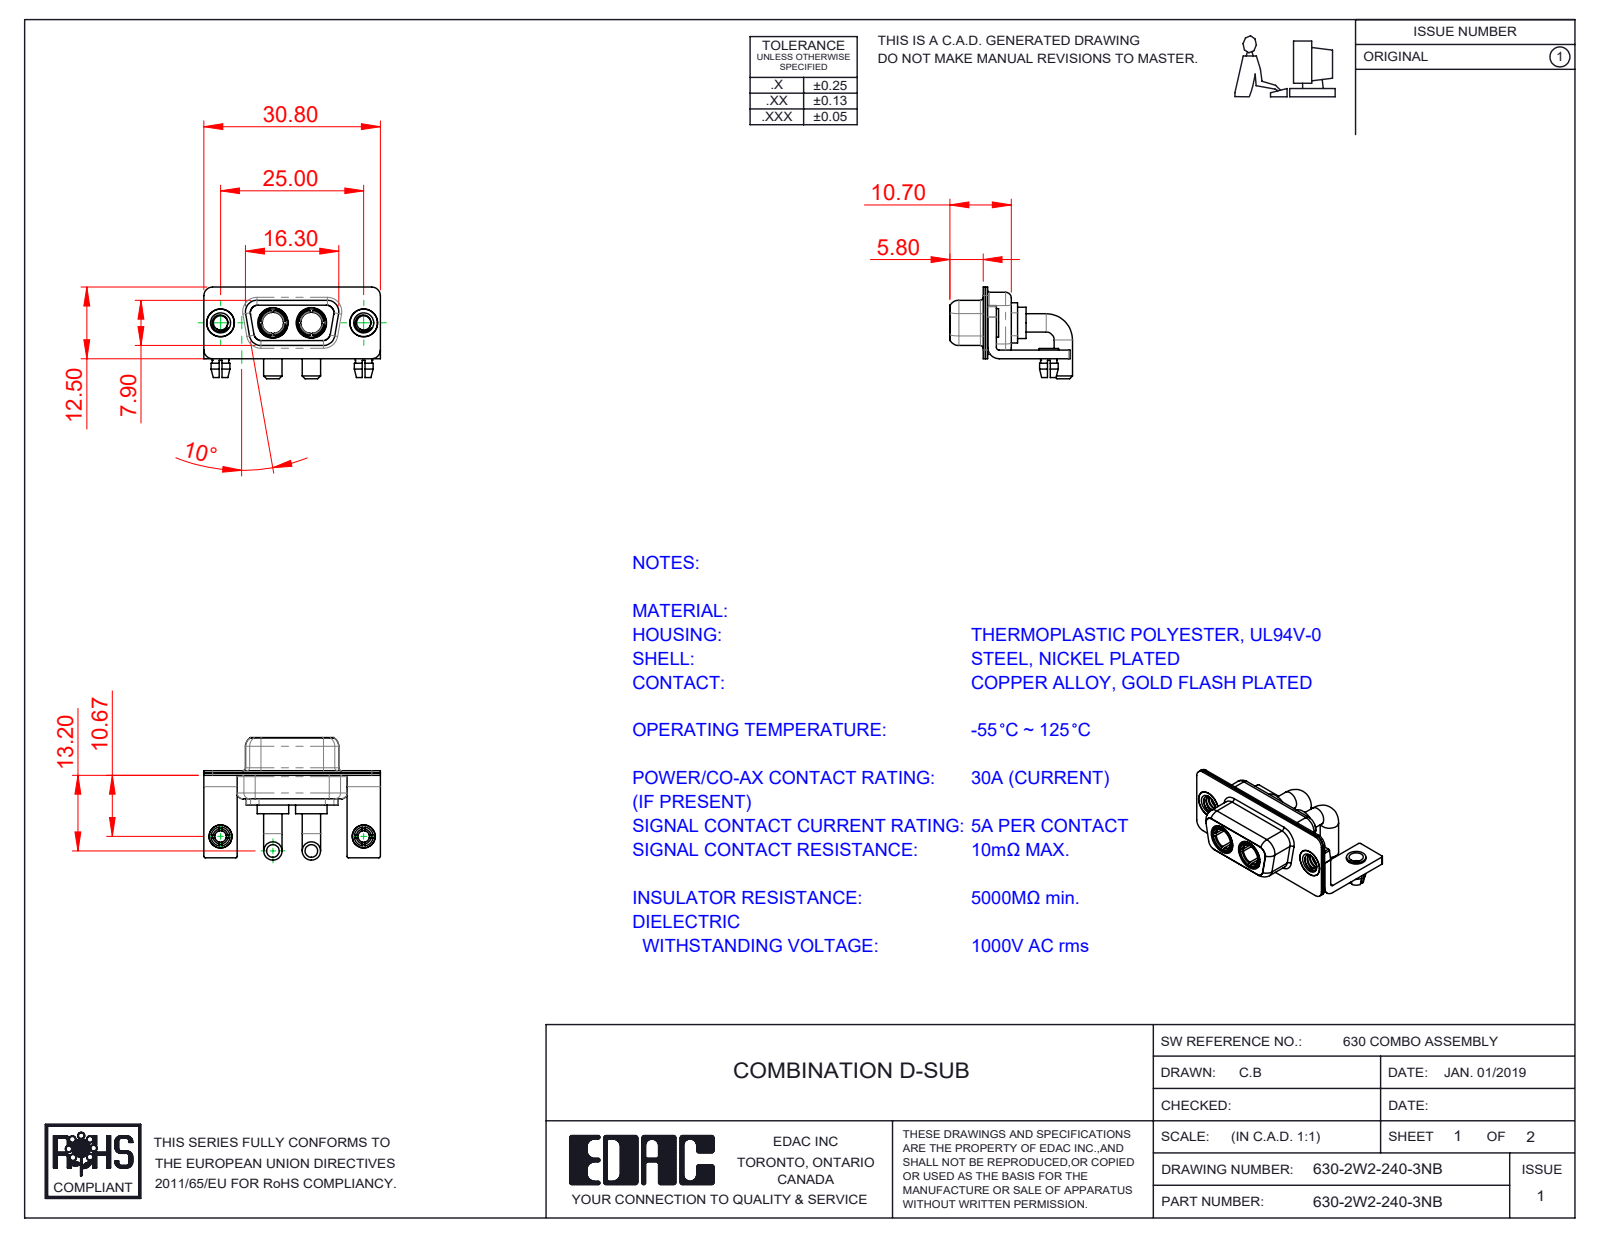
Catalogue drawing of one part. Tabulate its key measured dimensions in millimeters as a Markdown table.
| quantity | value |
| --- | --- |
| part name | 630Combo Shell Rear_09 Contacts; 630Combo Shell Front_09 Contacts; 630Combo Stabilizer Bracket; 630Combo Housing_2W2 (+4 more) |
| STEP written by | SolidWorks 2020 (CONFIG_CONTROL_DESIGN) |
| units | millimeters |
| bodies | 13 solids, 565 faces (193 planar, 237 cylindrical, 135 other) |
| overall size | 30.8 × 21.4 × 16 |
| volume | 2 161 mm³ |
| surface area | 5 228 mm² |
| round holes (diameter × count) | 2.5 × 4, 4.85 × 4, 2 × 2, 3.2 × 2, 3.7 × 2, 4 × 2, 4.05 × 2, 5.3 × 2 |
| round bosses / shafts (diameter × count) | 3.2 × 4, 5.5 × 2, 5.2 × 2, 5 × 2, 4.96 × 2, 4.95 × 2, 4.8 × 2, 4.75 × 2 |
| partial cylindrical surfaces (radius × count) | 0.25 × 16, 1.5 × 16, 2 × 13, 1.35 × 8, 1.6 × 8, 0.5 × 5, 0.6 × 4, 0.65 × 4 |
| main face-to-face distances | 0.4, 1.5, 0.8, 1.4, 0.45, 8.45, 1.8, 2.3, 8.9, 3.7 |
| hole center spacings | 9.14, 15.86, 25, 6.72 |
